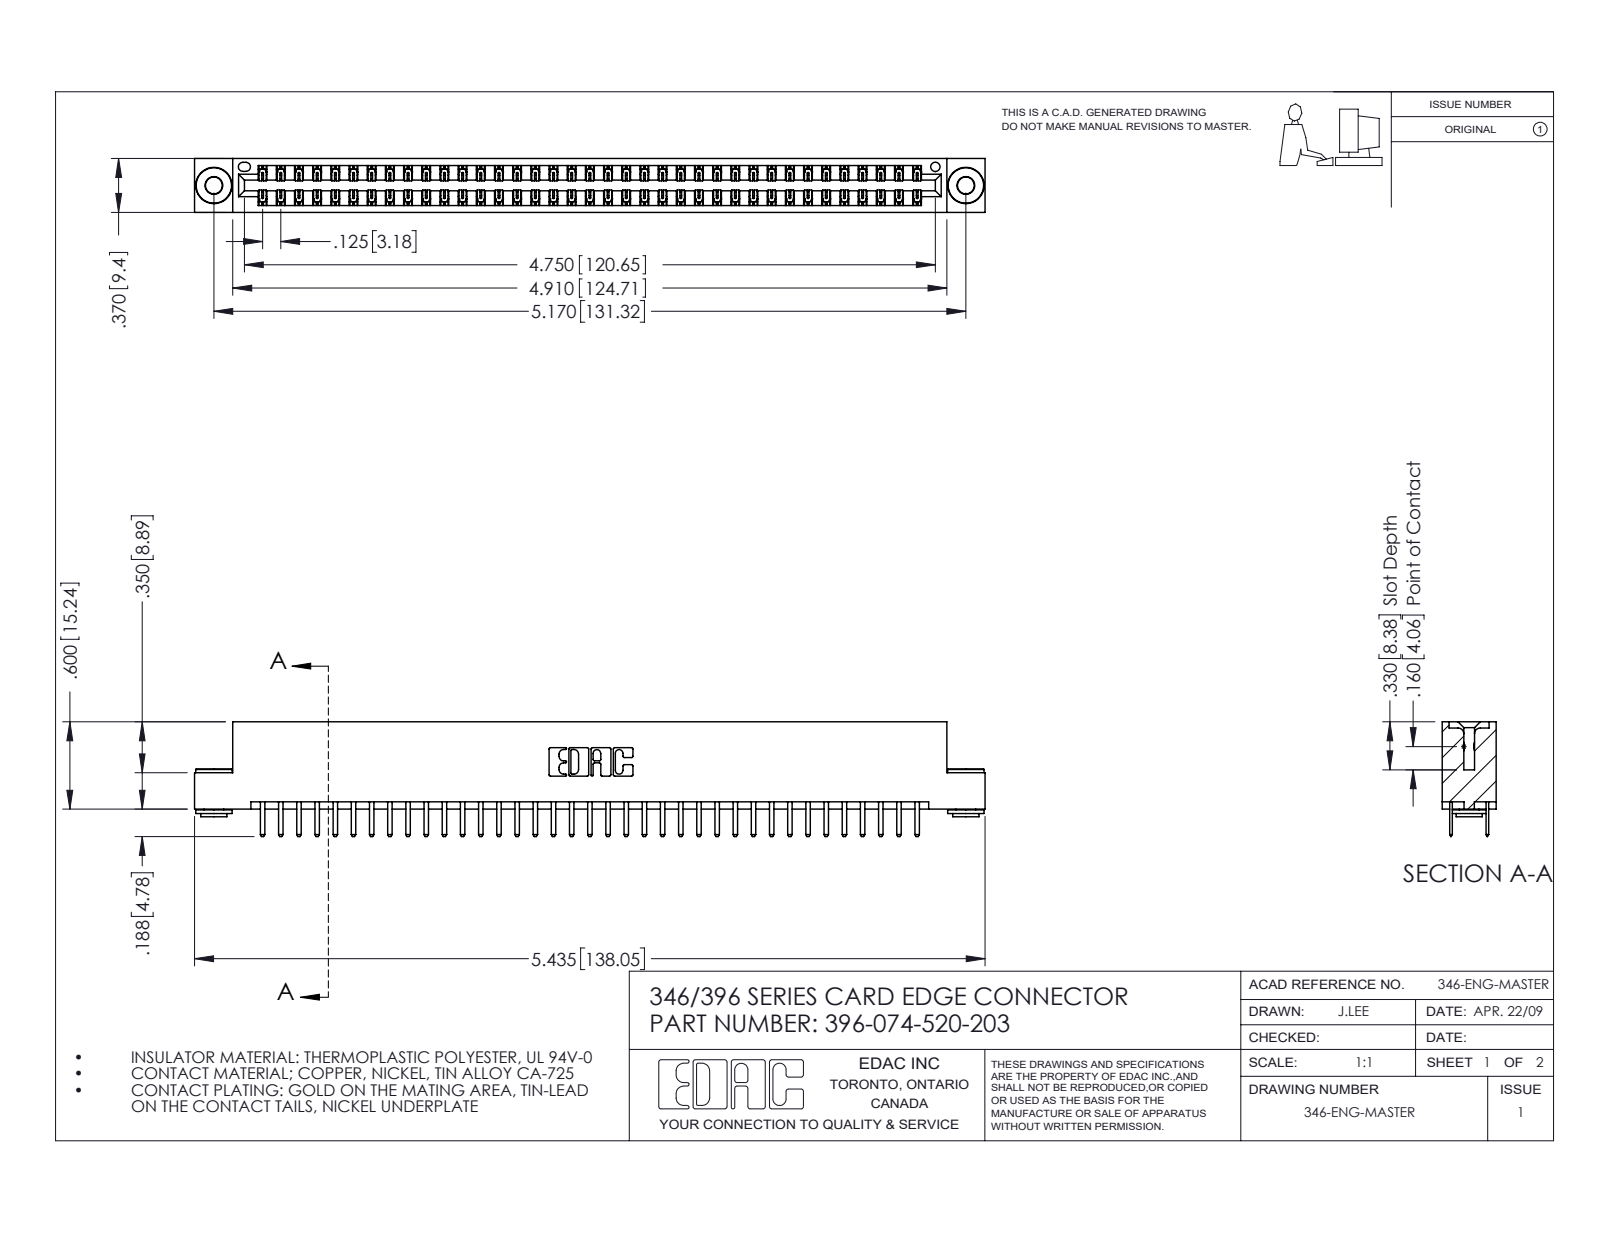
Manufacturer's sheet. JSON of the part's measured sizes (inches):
{"part_name": "345-250-002_345-250-002-102; 345-292-001_345-293-120; 346 Part_Flush Mounting Lugs - 0.156 Dia-TH; 396-074-520-203", "step_written_by": "SolidWorks 2016 (CONFIG_CONTROL_DESIGN)", "units": "inches", "bodies": {"solids": 77, "faces": 4304, "planar": 2824, "cylindrical": 1472, "other": 8}, "overall_size": [5.435, 0.788, 0.37], "volume_in3": 0.818, "surface_area_in2": 28.66, "round_holes": [[0.116, 2], [0.156, 2], [0.064, 1]], "round_bosses_or_shafts": [[0.25, 2], [0.18, 2], [0.136, 2]], "partial_cylinders_radius": [[0.006, 111], [0.01, 78], [0.01, 22], [0.007, 6], [0.031, 6], [0.026, 3], [0.014, 2], [0.022, 2]], "face_to_face_distances": [0.048, 0.322, 0.25, 0.37, 0.025, 0.275, 0.072, 0.298, 0.148, 0.222], "hole_center_spacings": [0.246, 4.961, 5.17]}
